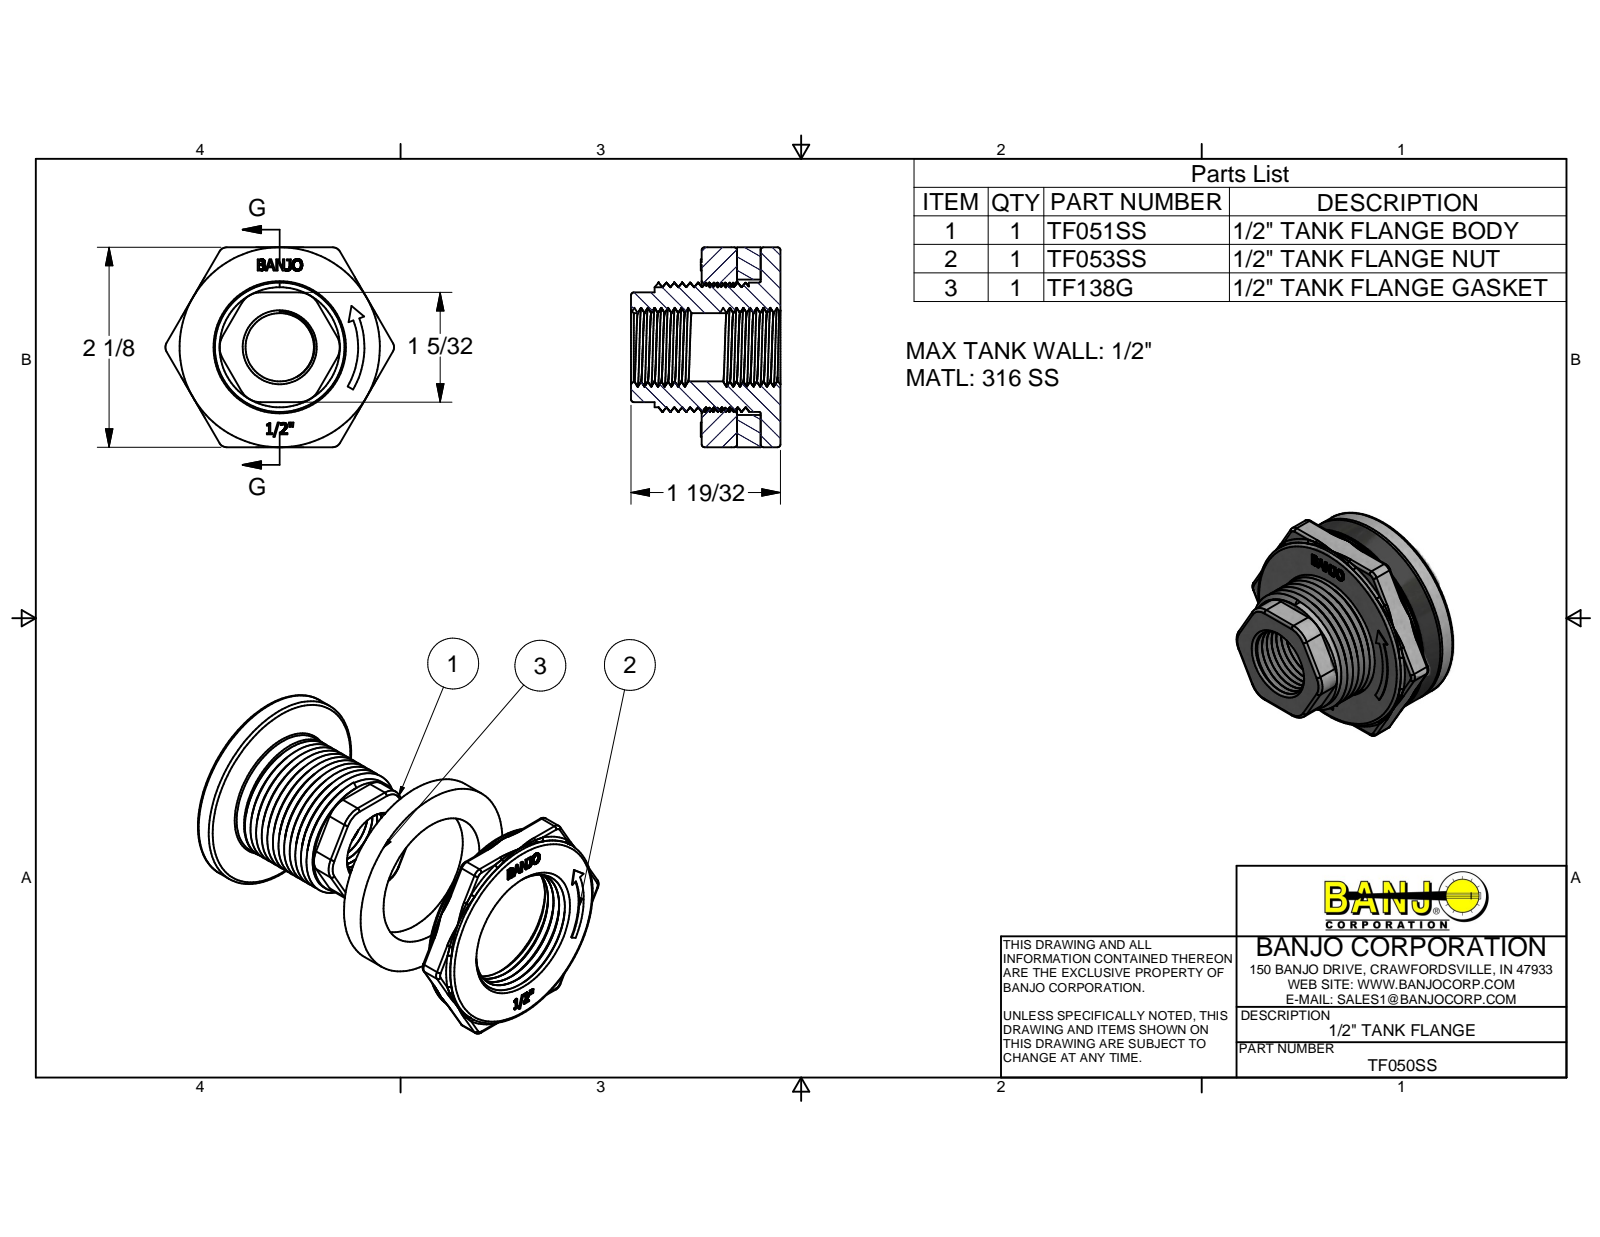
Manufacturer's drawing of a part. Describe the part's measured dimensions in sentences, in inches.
The part is named "TF050SS; TF051SS; TF053SS; TF138G". Its 3-D file was written by "Autodesk Inventor 2011 (AUTOMOTIVE_DESIGN)". It is 2 solids with 349 faces: 130 planar, 55 cylindrical and 164 other. Overall it measures 2.426 by 2.125 by 1.585 inches. Its volume is 1.372 cubic inches and its surface area 37.37 square inches. Round holes: 1 of diameter 0.726, 1 of diameter 1.285, 1 of diameter 1.437. Round bosses or shafts: 1 of diameter 2.125, 1 of diameter 1.375, 1 of diameter 1.276. Partial cylindrical surfaces (rounded edges, fillets, slot ends): 18 of radius 0.03, 6 of radius 0.09, 6 of radius 0.23, 1 of radius 0.832, 1 of radius 0.899. The main face-to-face distances are 0.25, 0.21, 0.46, 0.835, 0.625, 0.375, 1.125, 2.125, 1.585, 1.375.
